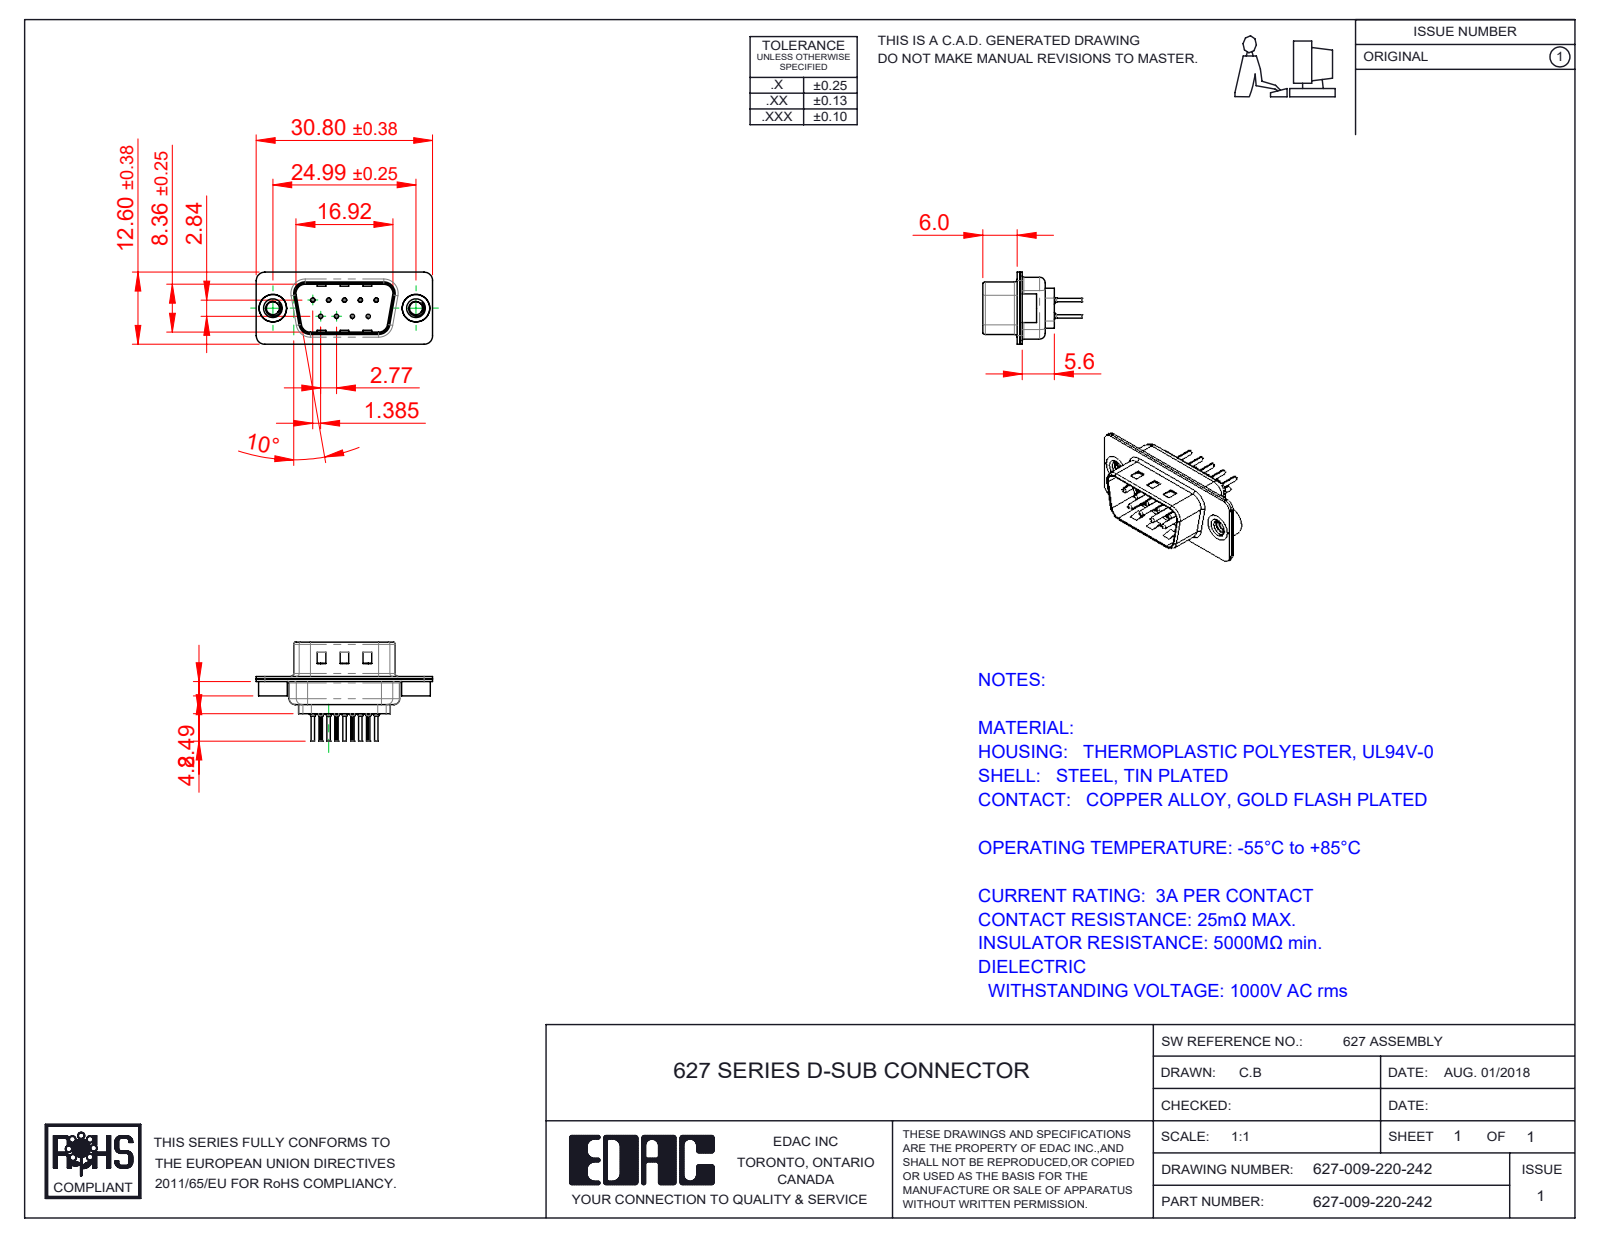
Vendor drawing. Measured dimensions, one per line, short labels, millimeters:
name: 627 Contact Row 1_20L; 627 Shell Front_09 Contacts; 627 Contact Row 2_20L; 627 4-40 Threaded Rivet (+3 more)
written by: SolidWorks 2020 (CONFIG_CONTROL_DESIGN)
unit: mm
bodies: 14 solids, 1182 faces (323 planar, 460 cylindrical, 399 other)
size: 30.8 × 17.3 × 12.6
volume: 1 307 mm³; area: 3 924 mm²
holes: 9× ⌀0.2, 9× ⌀0.35, 9× ⌀1.1, 9× ⌀1.6, 2× ⌀2.26, 2× ⌀4, 2× ⌀4.8
bosses: 9× ⌀2, 9× ⌀1.5, 9× ⌀0.75, 9× ⌀0.6, 2× ⌀5, 2× ⌀4.9
rounds: 18× R0.1, 18× R1.5, 12× R2, 8× R0.5, 8× R1.6, 4× R0.25, 4× R0.6, 4× R0.65
face distances: 0.45, 0.4, 0.9, 0.82, 9.58, 1.4, 8.76, 0.5, 1.5, 5.6
hole spacings: 3.16, 2.77, 5.54, 5.03, 5.04, 8.31, 7.48, 7.49
